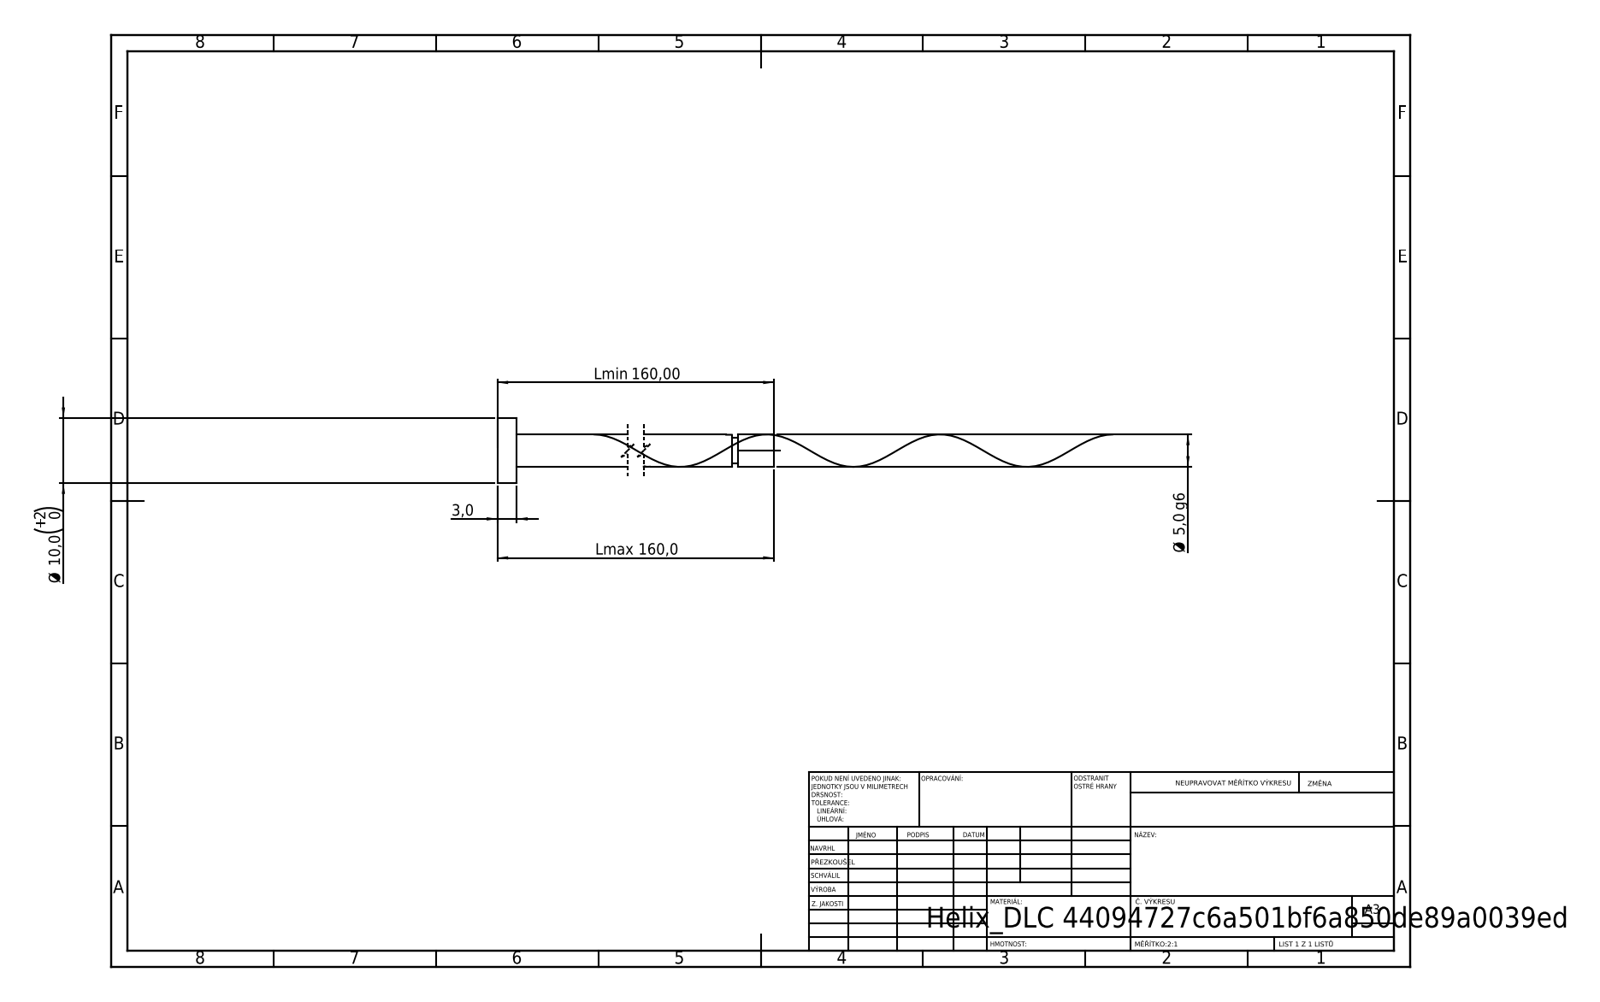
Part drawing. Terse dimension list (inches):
written by: SolidWorks 2019 (CONFIG_CONTROL_DESIGN)
unit: in
bodies: 1 solid, 21 faces (6 planar, 14 cylindrical, 1 other)
size: 6.299 × 0.394 × 0.394
volume: 0.2 in³; area: 4.301 in²
bosses: 1× ⌀0.394, 1× ⌀0.197, 1× ⌀0.157
face distances: 0.118, 6.299, 6.181, 6.083, 5.965, 0.216, 6.044, 5.926, 0.039, 0.255
